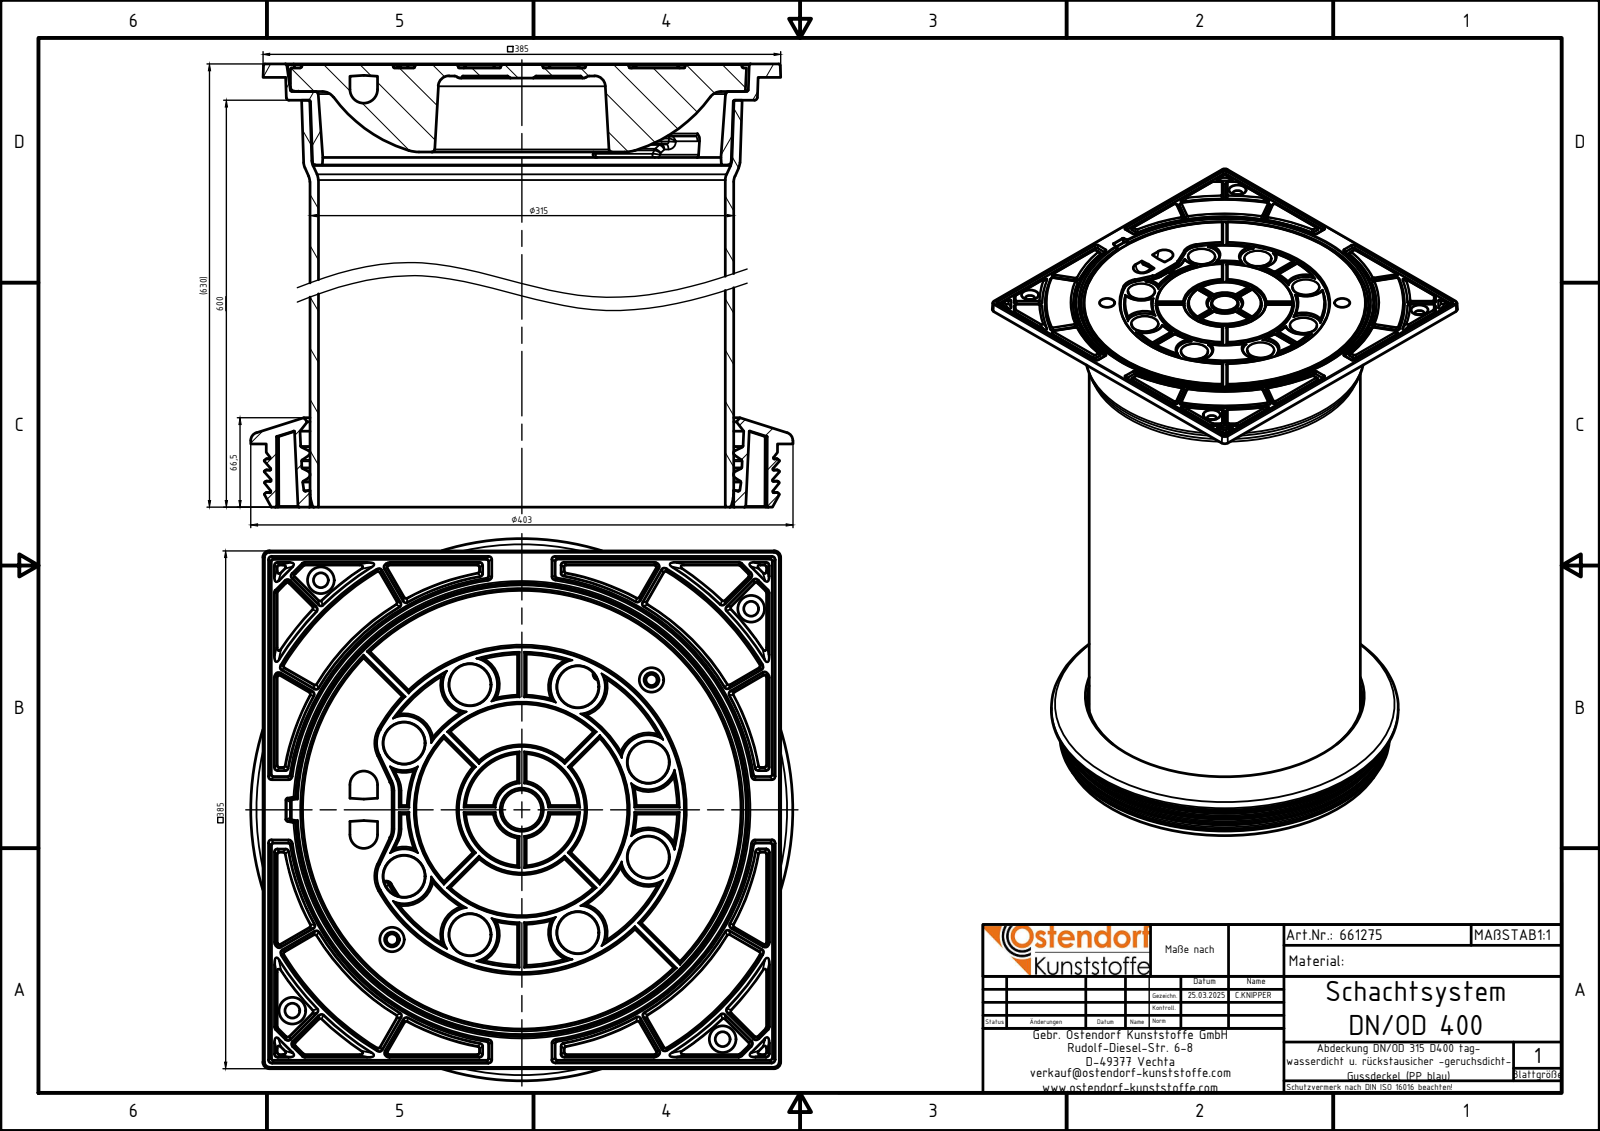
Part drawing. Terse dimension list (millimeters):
name: 661275z; 660300z; 990040z; 990040 Teil2z (+1 more)
written by: Autodesk Inventor 2024 (AUTOMOTIVE_DESIGN)
unit: mm
bodies: 4 solids, 1847 faces (247 planar, 375 cylindrical, 1225 other)
size: 626.53 × 403 × 403
volume: 8 795 000 mm³; area: 2 168 000 mm²
holes: 8× ⌀31, 6× ⌀11, 2× ⌀8.38, 2× ⌀18, 1× ⌀302.6, 1× ⌀315
bosses: 1× ⌀403, 1× ⌀380
rounds: 211× R1, 48× R2.5, 16× R0.5, 8× R4, 4× R2, 1× R3
face distances: 9.5, 0.5, 10, 10.5, 20.5, 20, 6.5, 2.5, 626.03, 17
hole spacings: 100.5, 226.75, 320.67, 65.44, 76.92, 80.15, 135.8, 136.5
